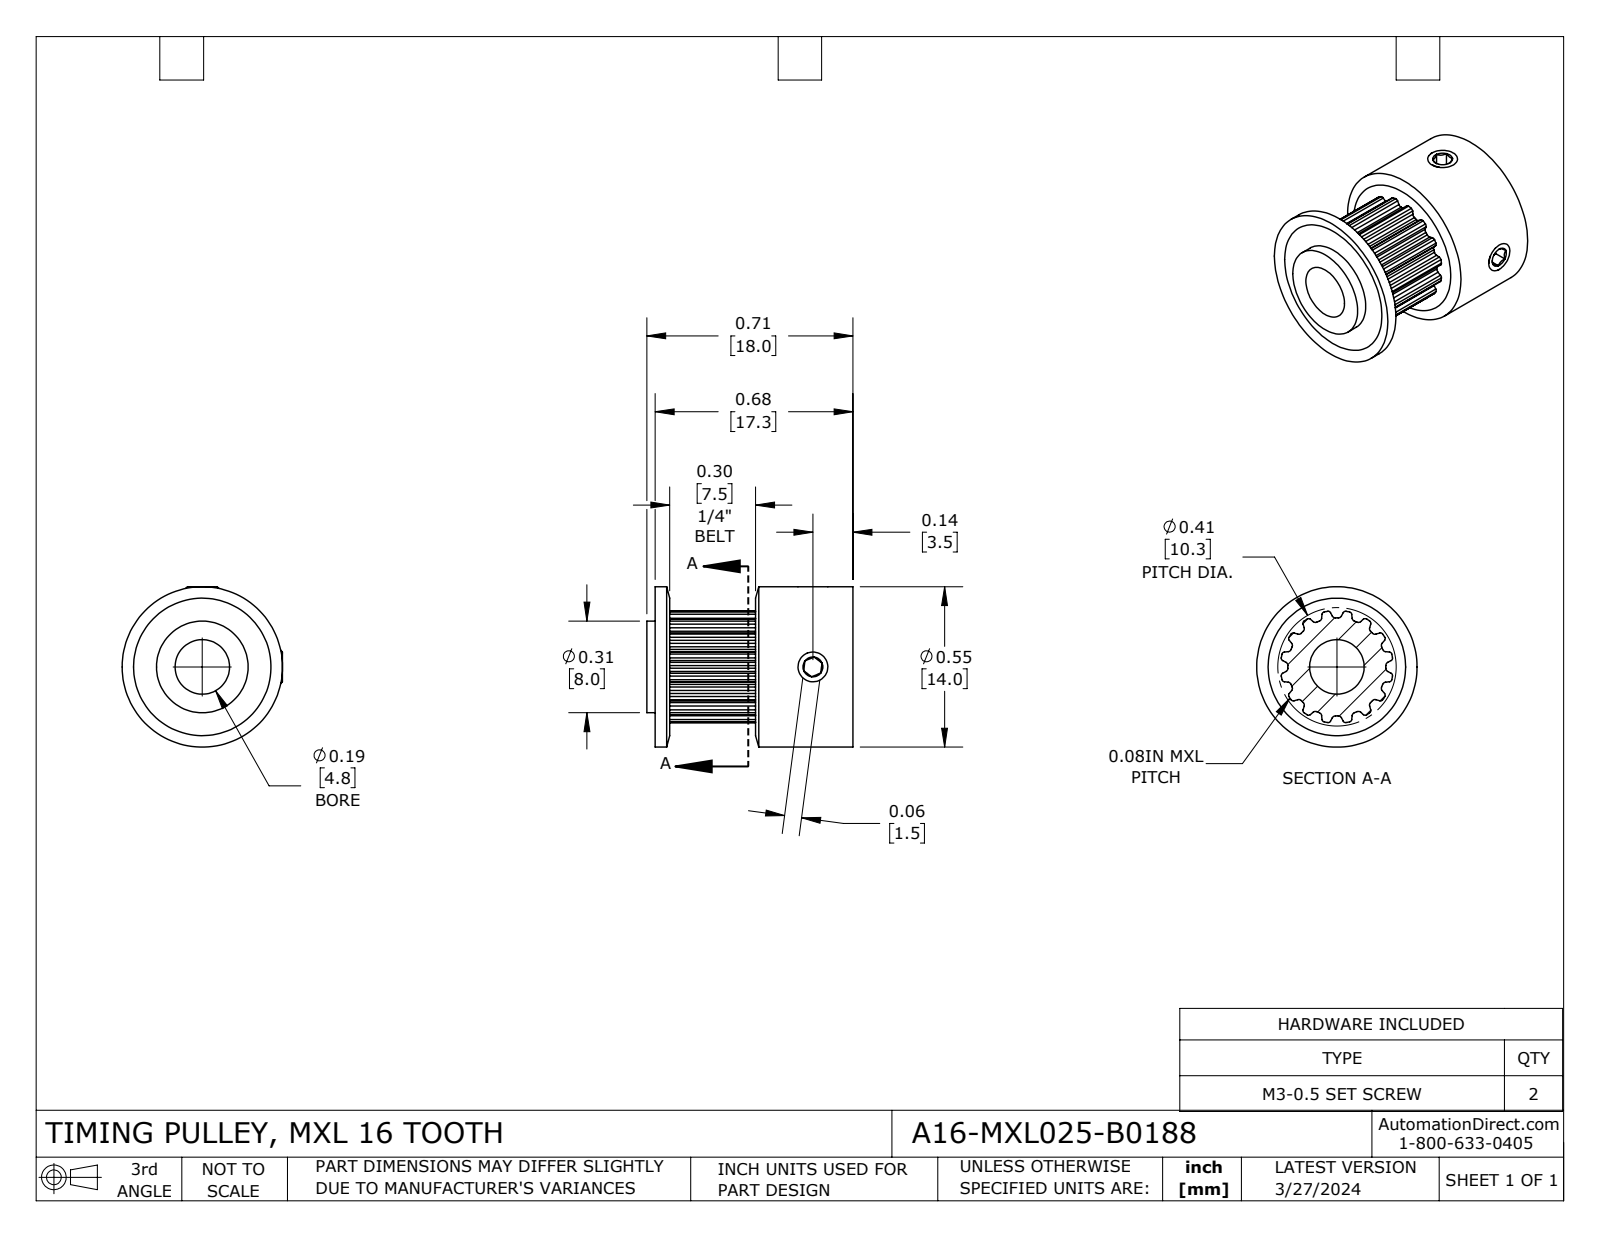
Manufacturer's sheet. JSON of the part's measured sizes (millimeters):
{"part_name": "A16-MXL025-B0188", "step_written_by": "SolidWorks 2021 (CONFIG_CONTROL_DESIGN)", "units": "millimeters", "bodies": {"solids": 3, "faces": 210, "planar": 53, "cylindrical": 125, "other": 32}, "overall_size": [18, 14, 14], "volume_mm3": 1674, "surface_area_mm2": 1594, "round_holes": [[2.5, 2], [4.76, 1]], "round_bosses_or_shafts": [[3, 2], [14, 1], [8, 1]], "partial_cylinders_radius": [[0.23, 32], [0.3, 32], [4.28, 1], [4.92, 1]], "face_to_face_distances": [8.5, 1, 17, 16, 7.5, 2, 9.5, 18, 3.48, 3.46]}
